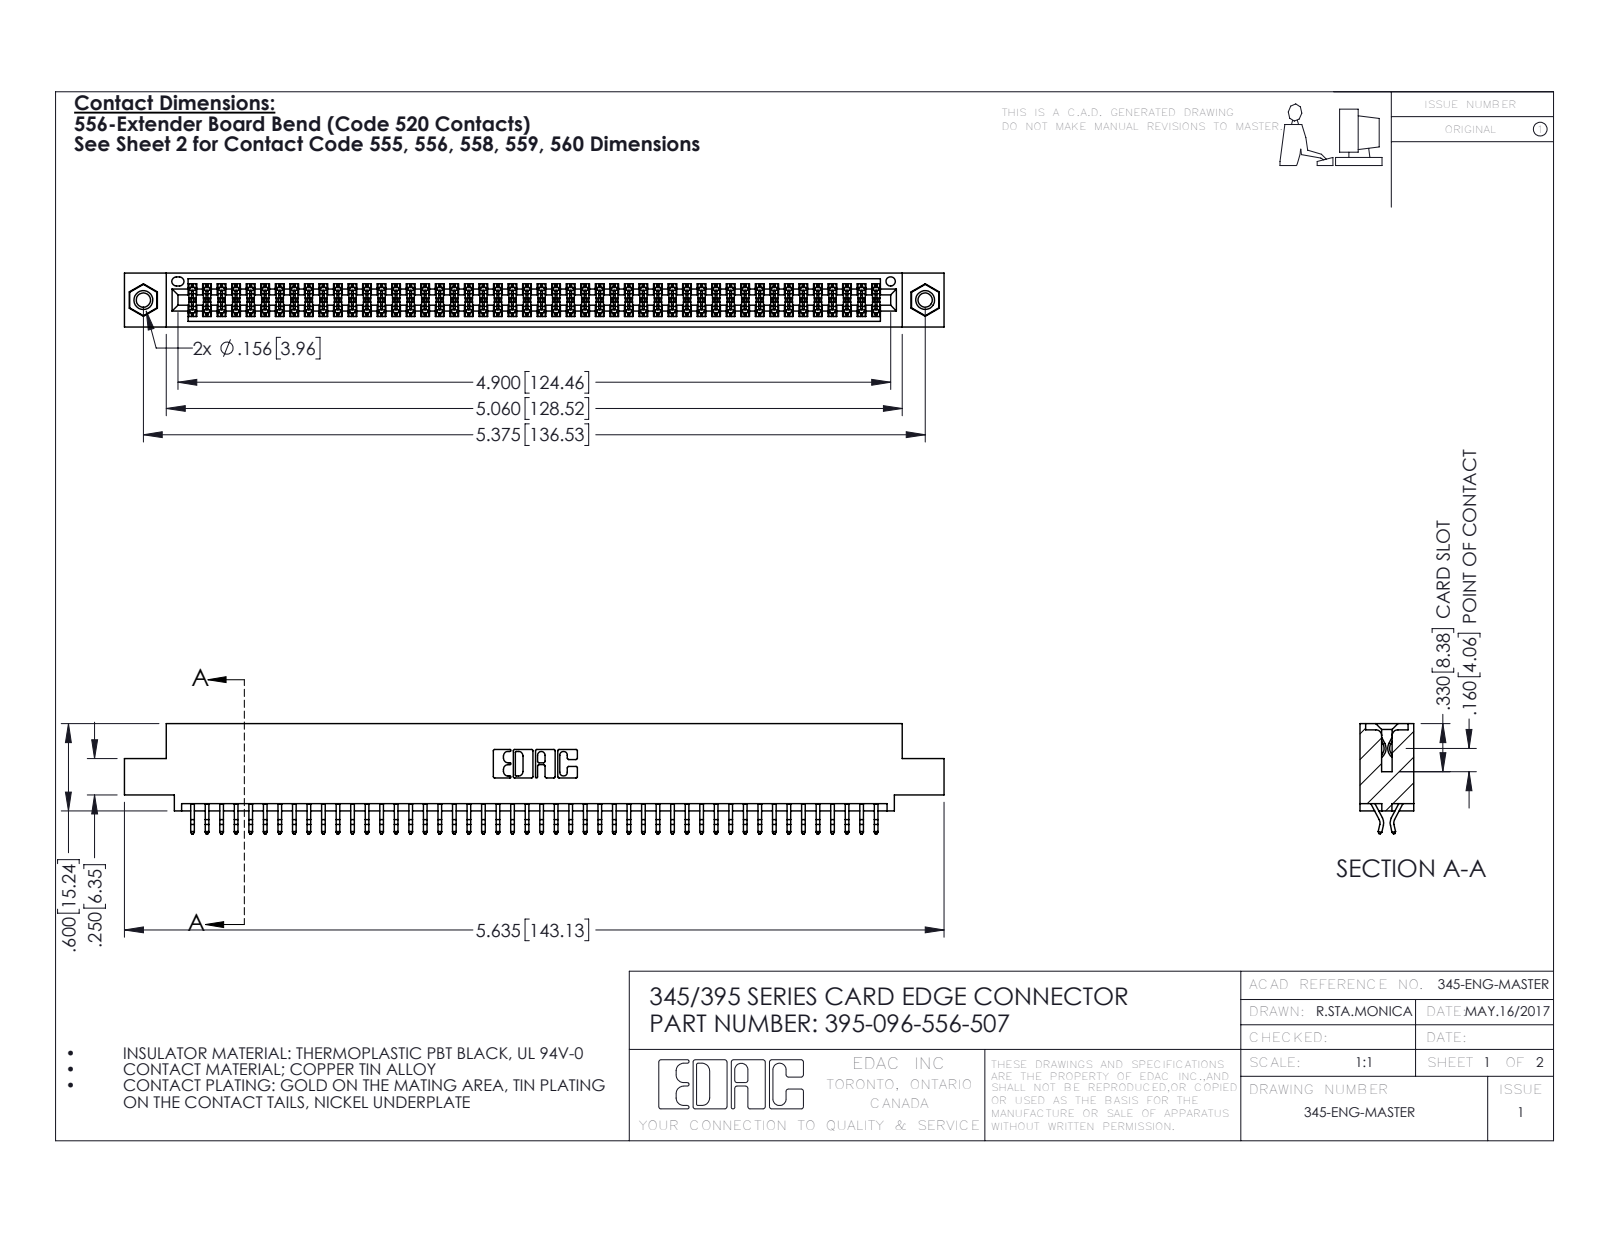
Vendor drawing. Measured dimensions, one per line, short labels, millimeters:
name: 345-292-001_556 Tail; 395-096-556-507; 345 Part_0.110 Offset - 0.156 Dia-TI; 345-250-001_345-250-005-103
written by: SolidWorks 2016 (CONFIG_CONTROL_DESIGN)
unit: mm
bodies: 99 solids, 5566 faces (3668 planar, 1882 cylindrical, 16 other)
size: 143.1 × 19.2 × 9.4
volume: 13 900 mm³; area: 20 650 mm²
holes: 2× ⌀2.5, 2× ⌀3.2, 2× ⌀4, 1× ⌀1.6
bosses: 2× ⌀3.9
rounds: 144× R0.2, 22× R0.3, 6× R0.2, 6× R0.8, 3× R0.7, 2× R0.3, 2× R0.4, 2× R0.5
face distances: 1.8, 7.6, 9.4, 5.1, 0.6, 2.5, 6.9, 5.7, 4.4, 3.8
hole spacings: 6.9, 130.5, 136.5
